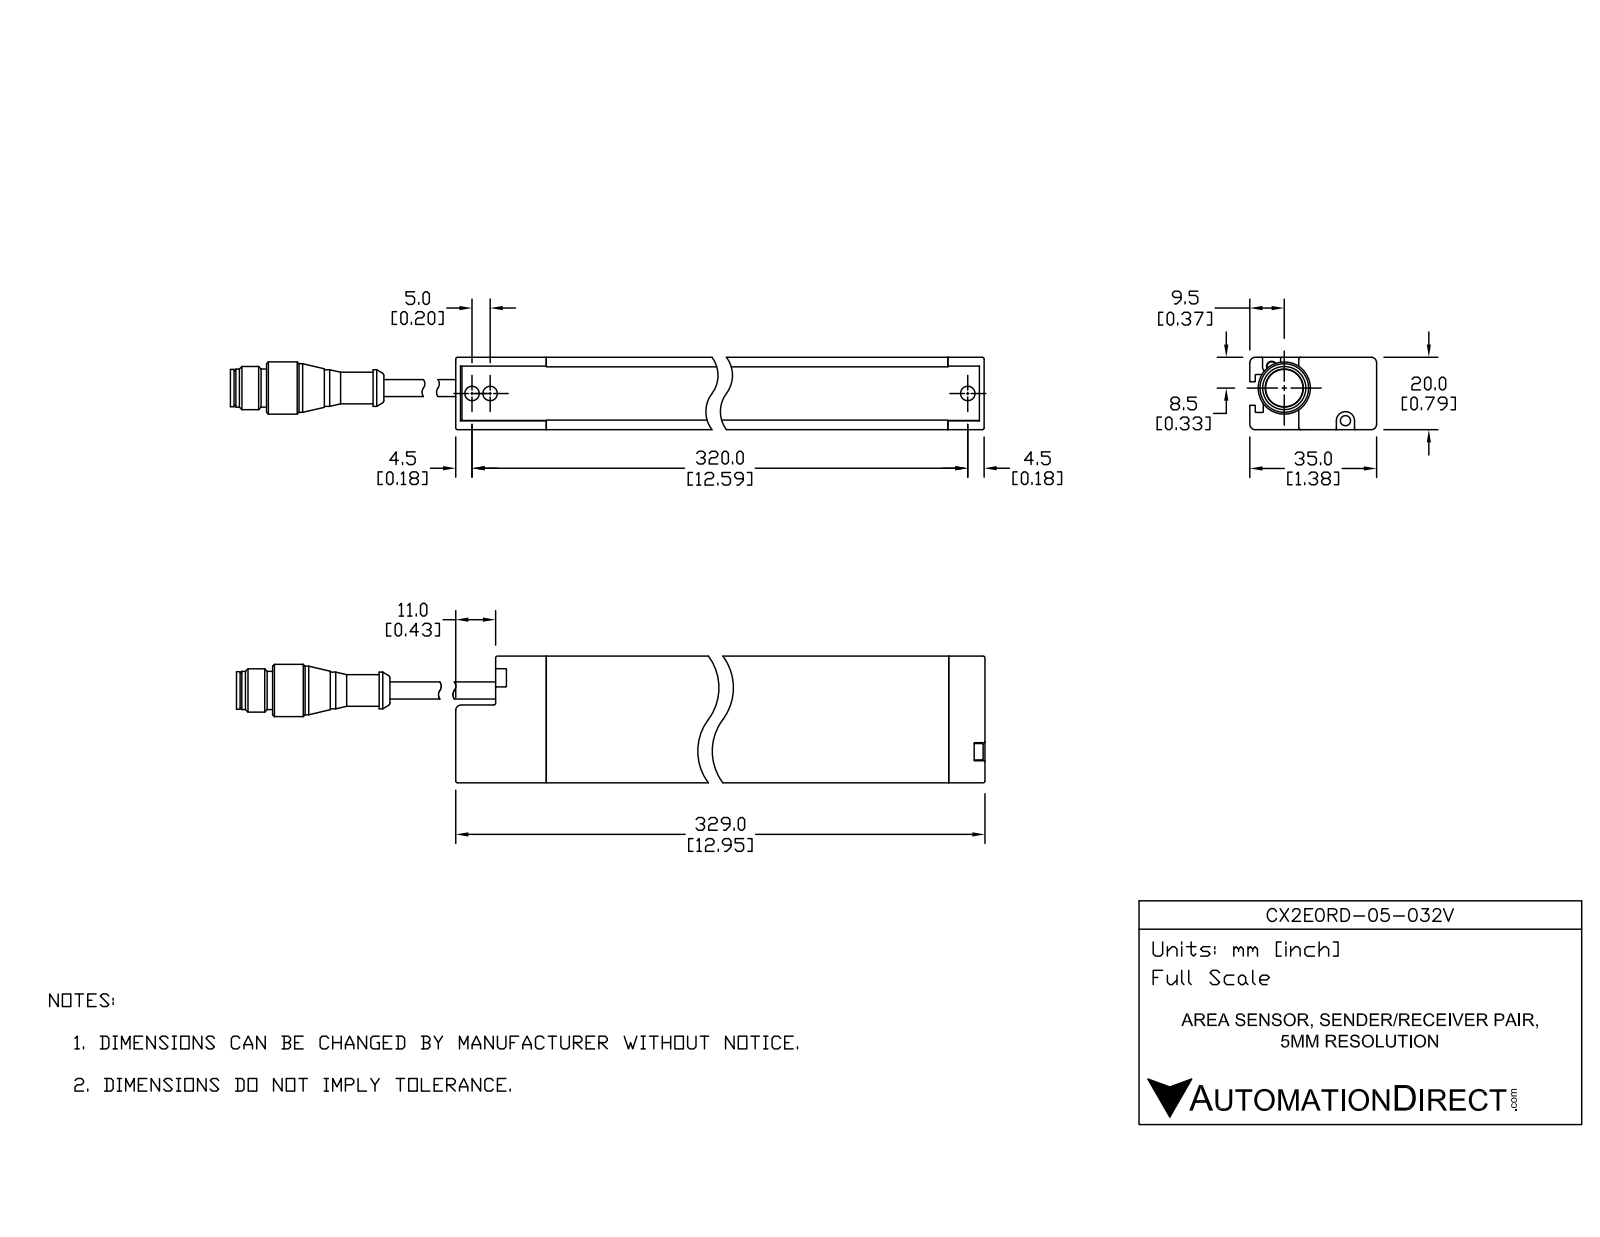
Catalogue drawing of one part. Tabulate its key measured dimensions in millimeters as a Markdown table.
| quantity | value |
| --- | --- |
| STEP written by | Unknown (AUTOMOTIVE_DESIGN) |
| units | millimeters |
| bodies | 16 solids, 688 faces (226 planar, 266 cylindrical, 196 other) |
| overall size | 737.18 × 638.71 × 481 |
| volume | 457 504 mm³ |
| surface area | 116 308 mm² |
| round holes (diameter × count) | 2.8 × 8, 6.5 × 2, 8 × 2 |
| round bosses / shafts (diameter × count) | 2.01 × 8, 4.5 × 4, 2.5 × 4, 14.42 × 2, 13.42 × 2, 11.93 × 2, 10.53 × 2, 10.33 × 2 |
| partial cylindrical surfaces (radius × count) | 0.2 × 96, 0.5 × 26, 1.5 × 10, 2.5 × 8, 0.3 × 4 |
| main face-to-face distances | 618.71, 20, 2, 638.71, 598.71, 669.88, 30.9, 698.88, 3.7, 34.6 |
| hole center spacings | 15, 20.4, 25.32, 937.83, 6.95, 9.66, 17.93, 19.15 |
